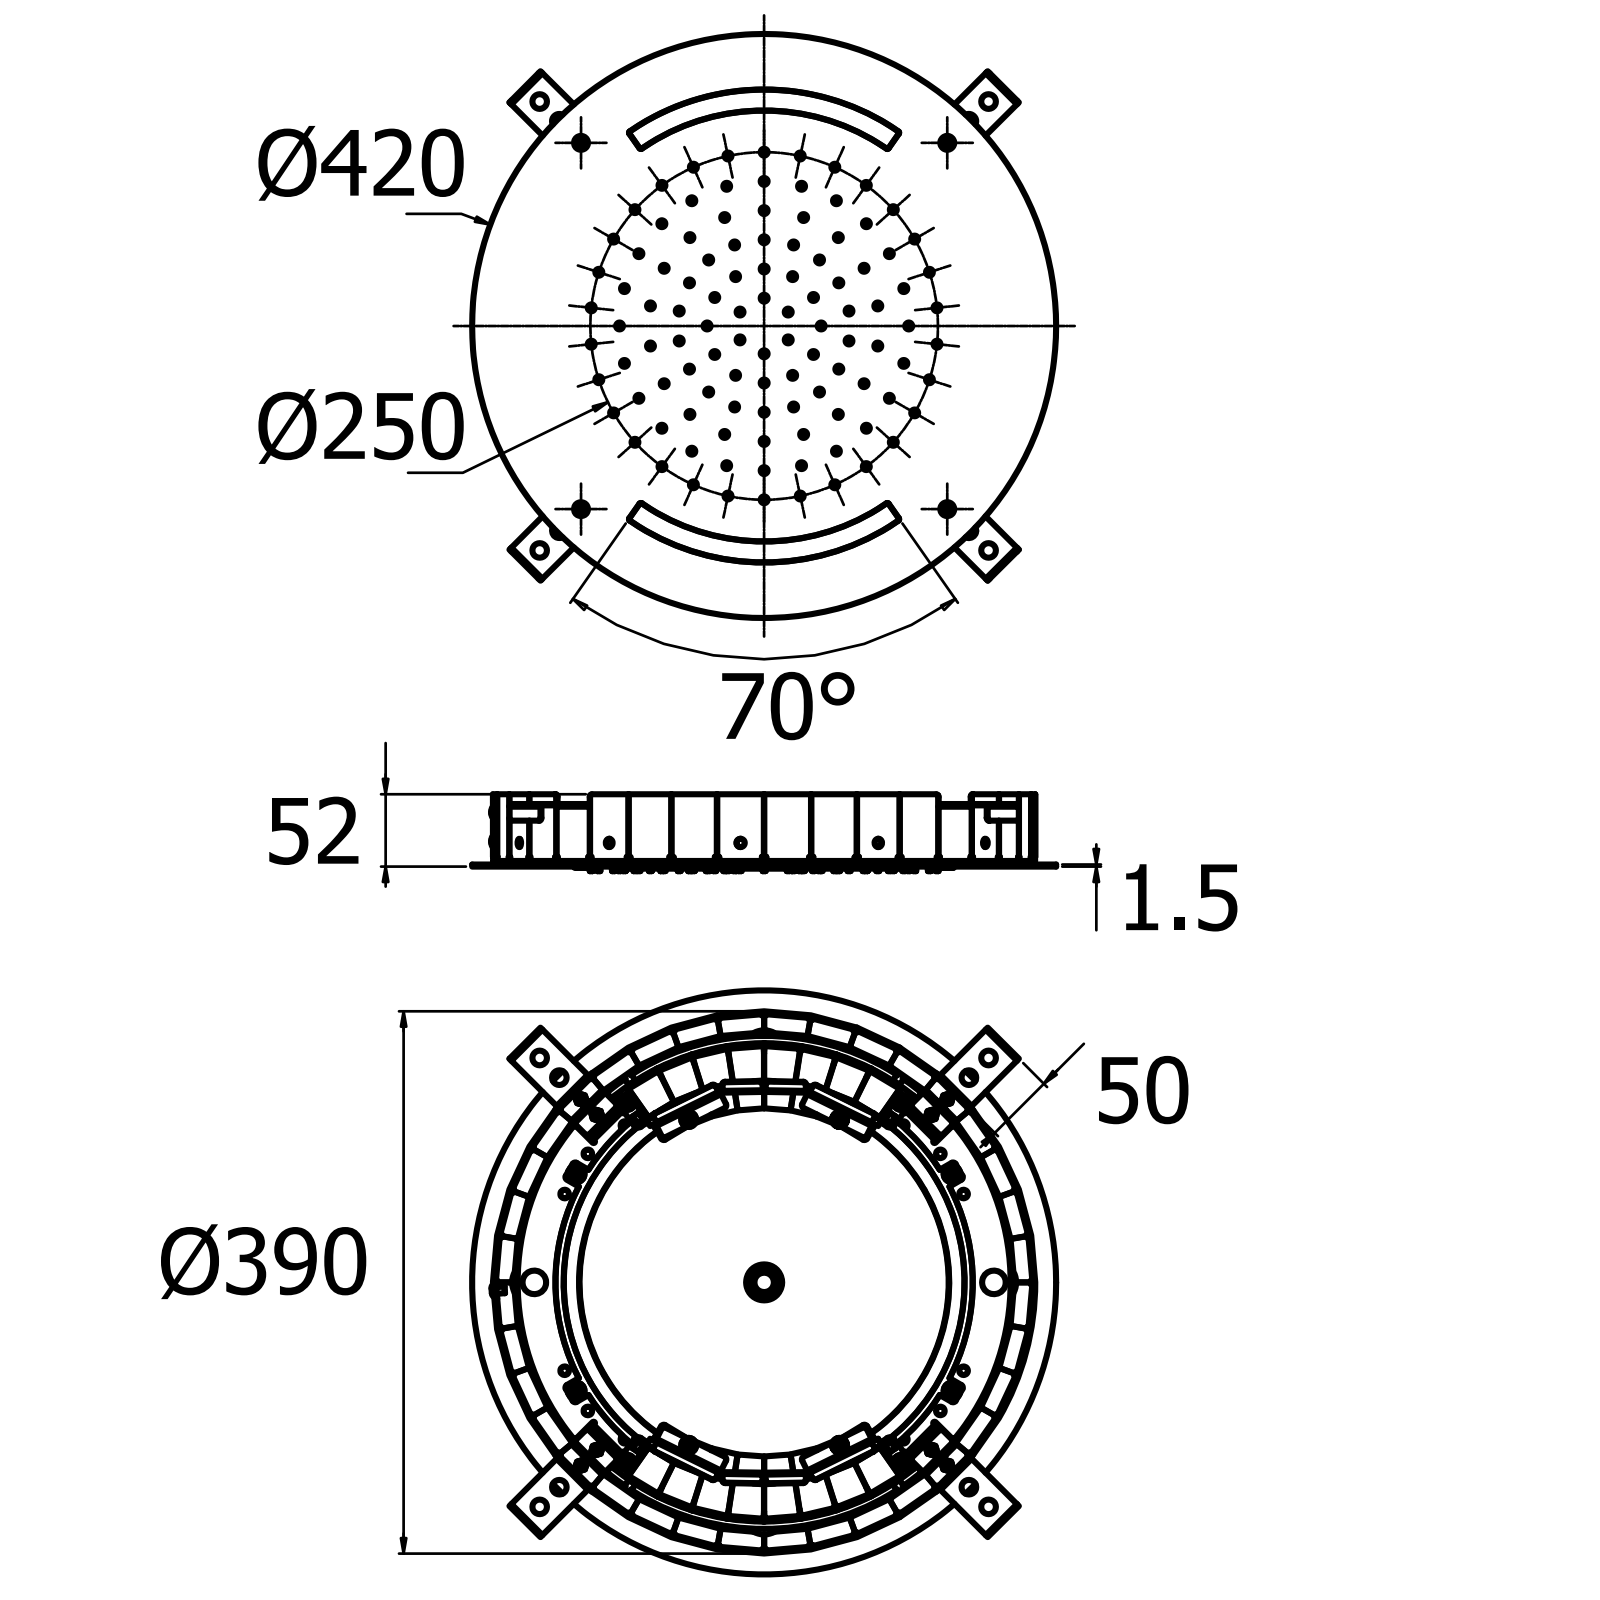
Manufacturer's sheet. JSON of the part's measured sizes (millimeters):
{"step_written_by": "ST-DEVELOPER v16.5 (AUTOMOTIVE_DESIGN)", "units": "millimeters", "bodies": {"solids": 0, "faces": 5413, "planar": 2240, "cylindrical": 0, "other": 3173}, "overall_size": [420, 420, 55.3], "face_to_face_distances": [1, 4, 3, 2.5, 1.5, 6.5, 0.5, 5, 5.5, 3.5]}
